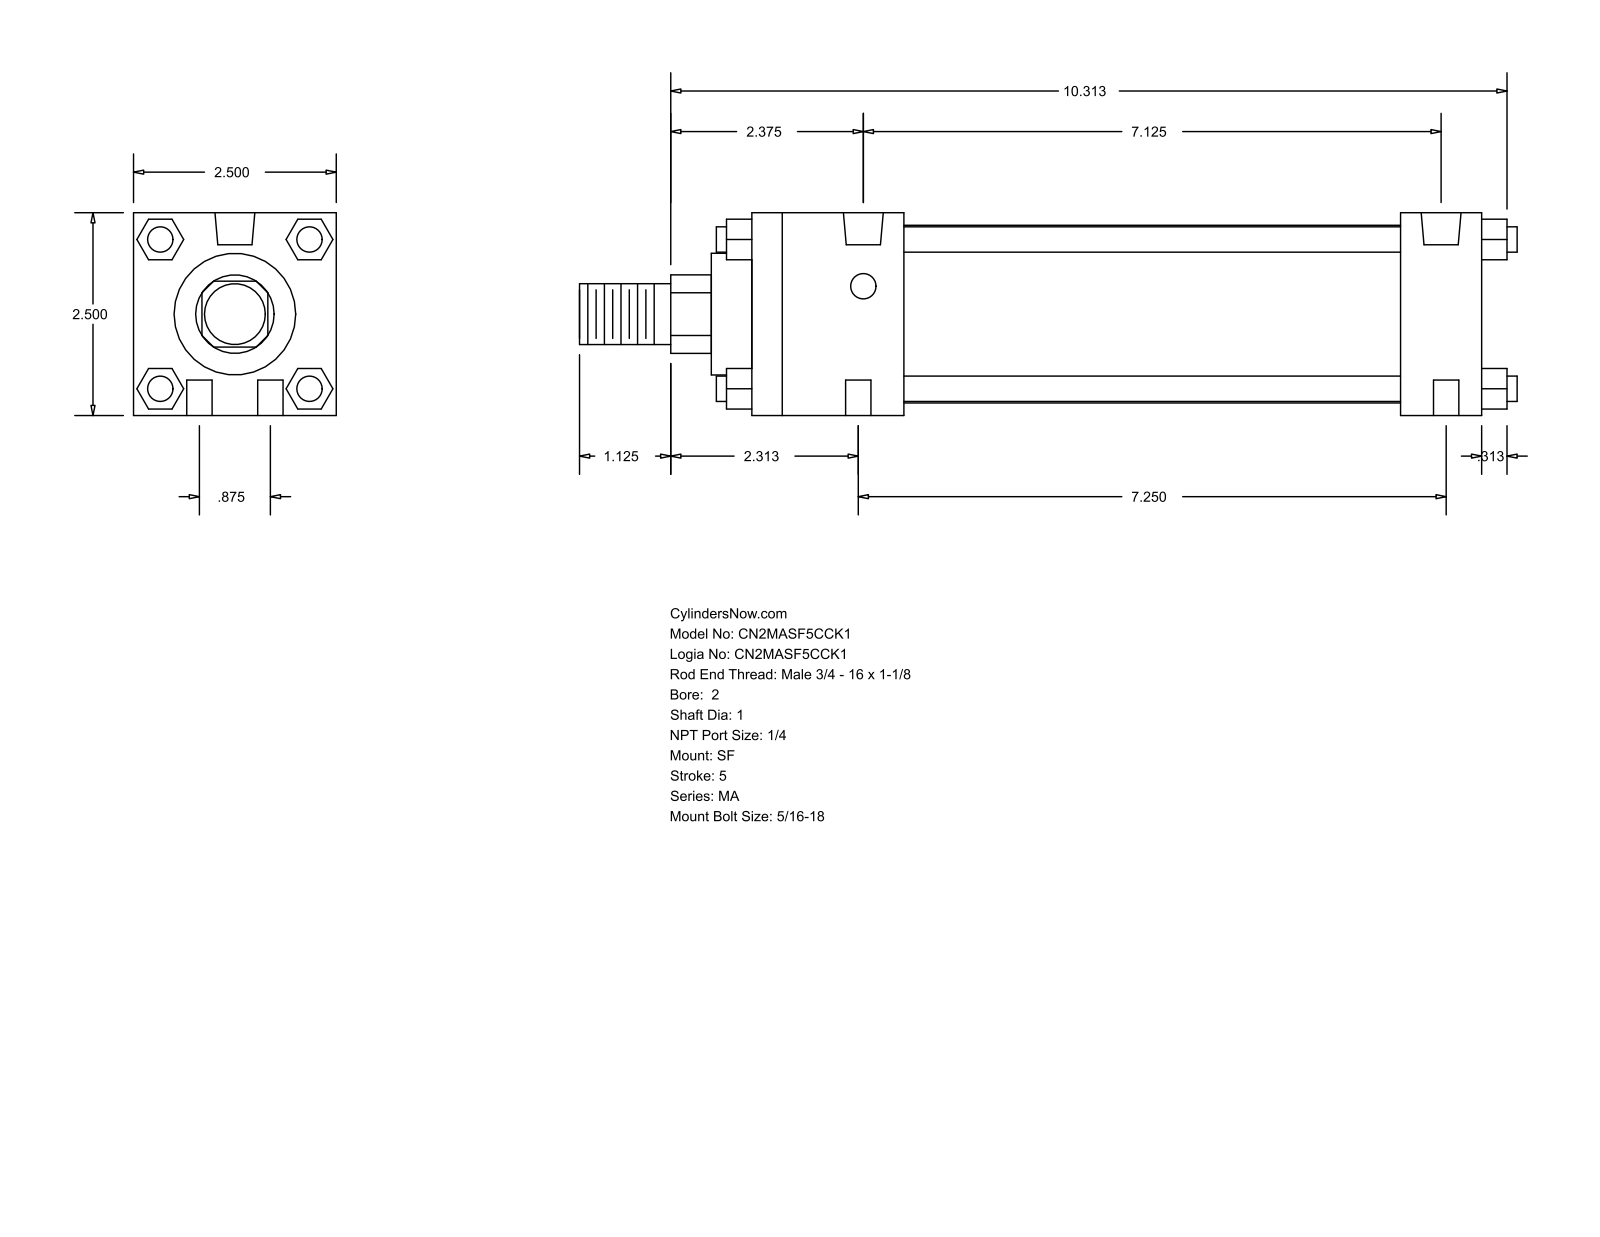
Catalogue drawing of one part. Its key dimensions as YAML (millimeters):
part_name: "MA_SF__0200_1"
step_written_by: "GSSL Pune (CONFIG_CONTROL_DESIGN)"
units: millimeters
bodies: {solids: 0, faces: 124, planar: 94, cylindrical: 30, other: 0}
overall_size: [293.69, 63.5, 63.5]
round_holes:
  - {diameter: 7.94, count: 6}
  - {diameter: 12.49, count: 2}
round_bosses_or_shafts:
  - {diameter: 7.94, count: 4}
  - {diameter: 55.63, count: 1}
  - {diameter: 38.1, count: 1}
  - {diameter: 25.4, count: 1}
  - {diameter: 19.05, count: 1}
partial_cylinders:
  - {radius: 12.29, count: 1}
face_to_face_distances: [63.5, 228.6, 12.7, 25.4, 203.2, 47.63, 155.57, 180.97, 40.47, 23.37]
hole_center_spacings: [11.22, 182.9, 22.22, 180.97, 184.15, 185.49]
